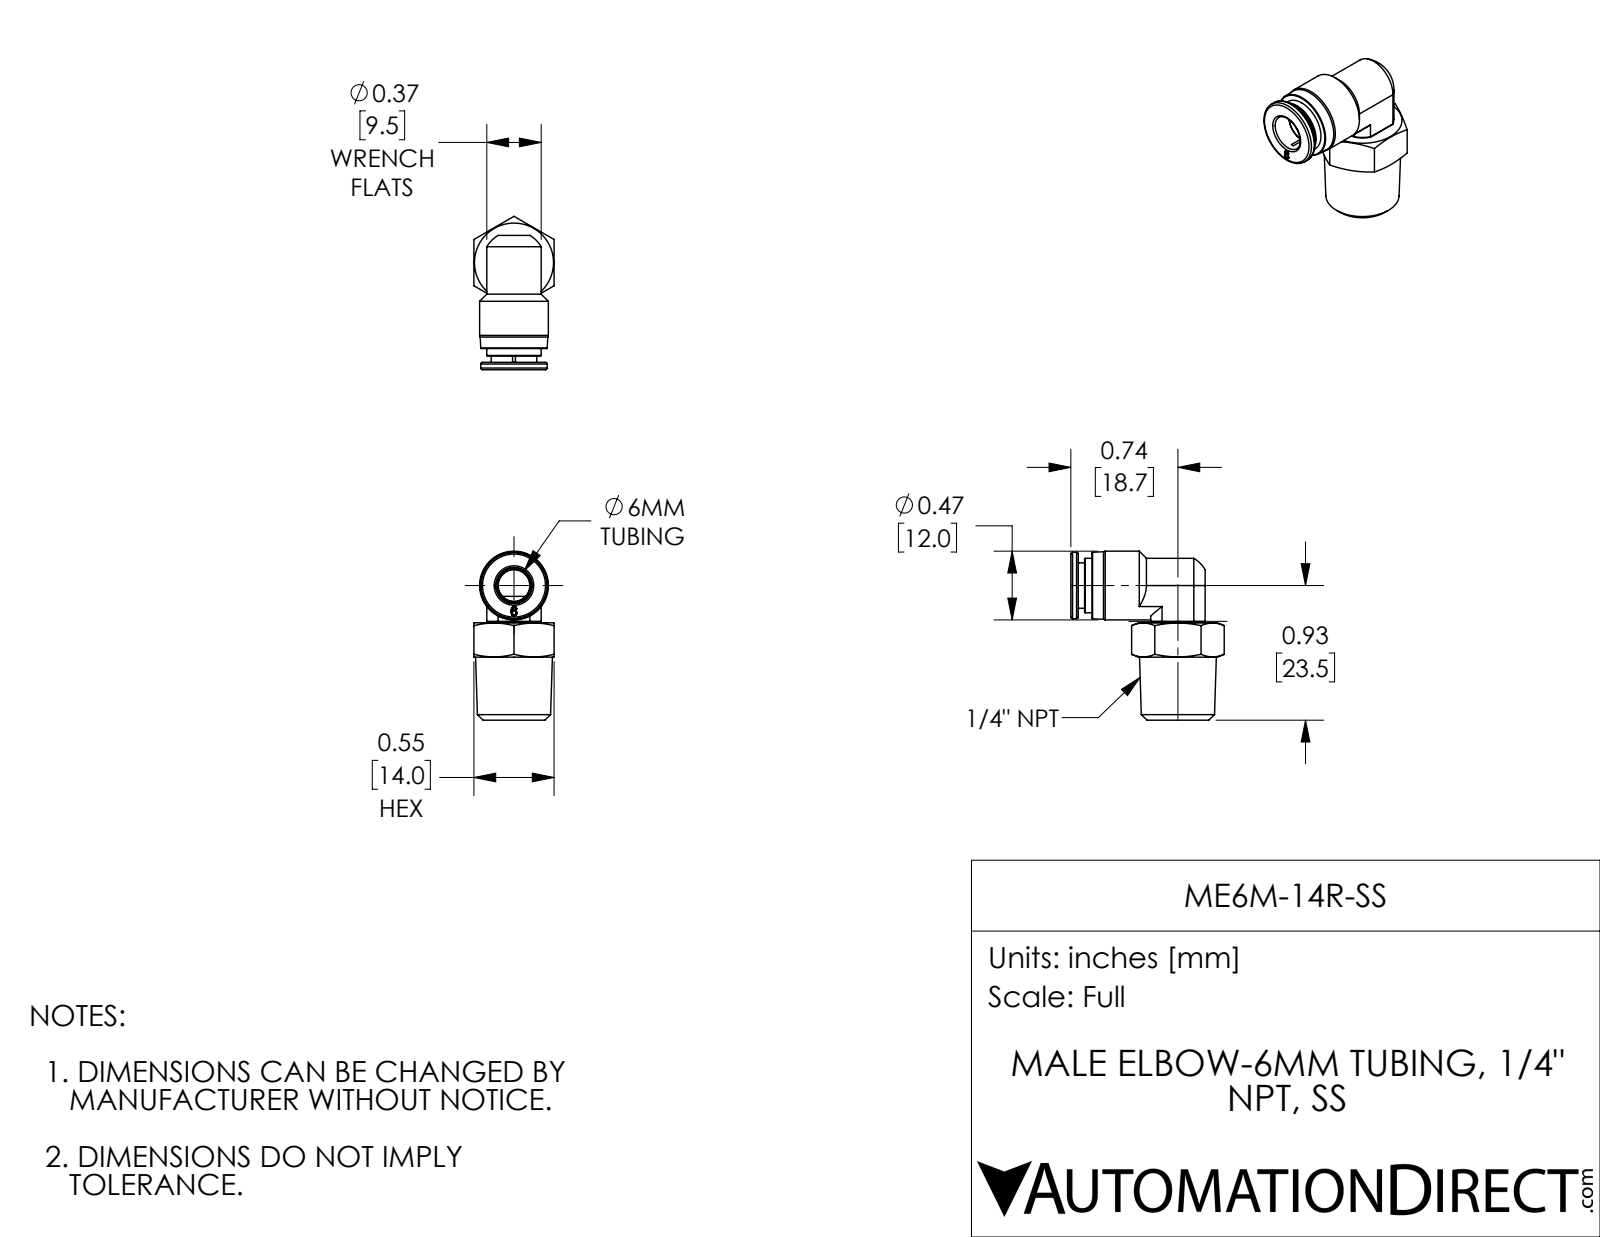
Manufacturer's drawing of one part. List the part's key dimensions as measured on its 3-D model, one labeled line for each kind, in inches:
Part name (STEP PRODUCT): ME6M-14R-SS
STEP written by: SolidWorks 2017 (AUTOMOTIVE_DESIGN)
Units: inches
Bodies: 2 solids, 122 faces (31 planar, 33 cylindrical, 58 other)
Overall size (bounding box): 1.161 × 1.054 × 0.551
Volume: 0.236 in³ · Surface area: 4.794 in²
Round holes (diameter × count): ⌀0.157 ×1, ⌀0.217 ×1, ⌀0.238 ×1, ⌀0.244 ×1, ⌀0.248 ×1, ⌀0.319 ×1
Round bosses / shafts (diameter × count): ⌀0.472 ×1, ⌀0.457 ×1, ⌀0.374 ×1, ⌀0.313 ×1, ⌀0.236 ×1
Partial cylindrical surfaces — rounded edges, fillets, slot ends (radius × count): R0.008 ×4, R0.217 ×1
Main face-to-face distances: 0.551, 0.089, 0.463, 0.669, 0.374, 0.051, 0.671, 0.923, 0.872, 0.094
